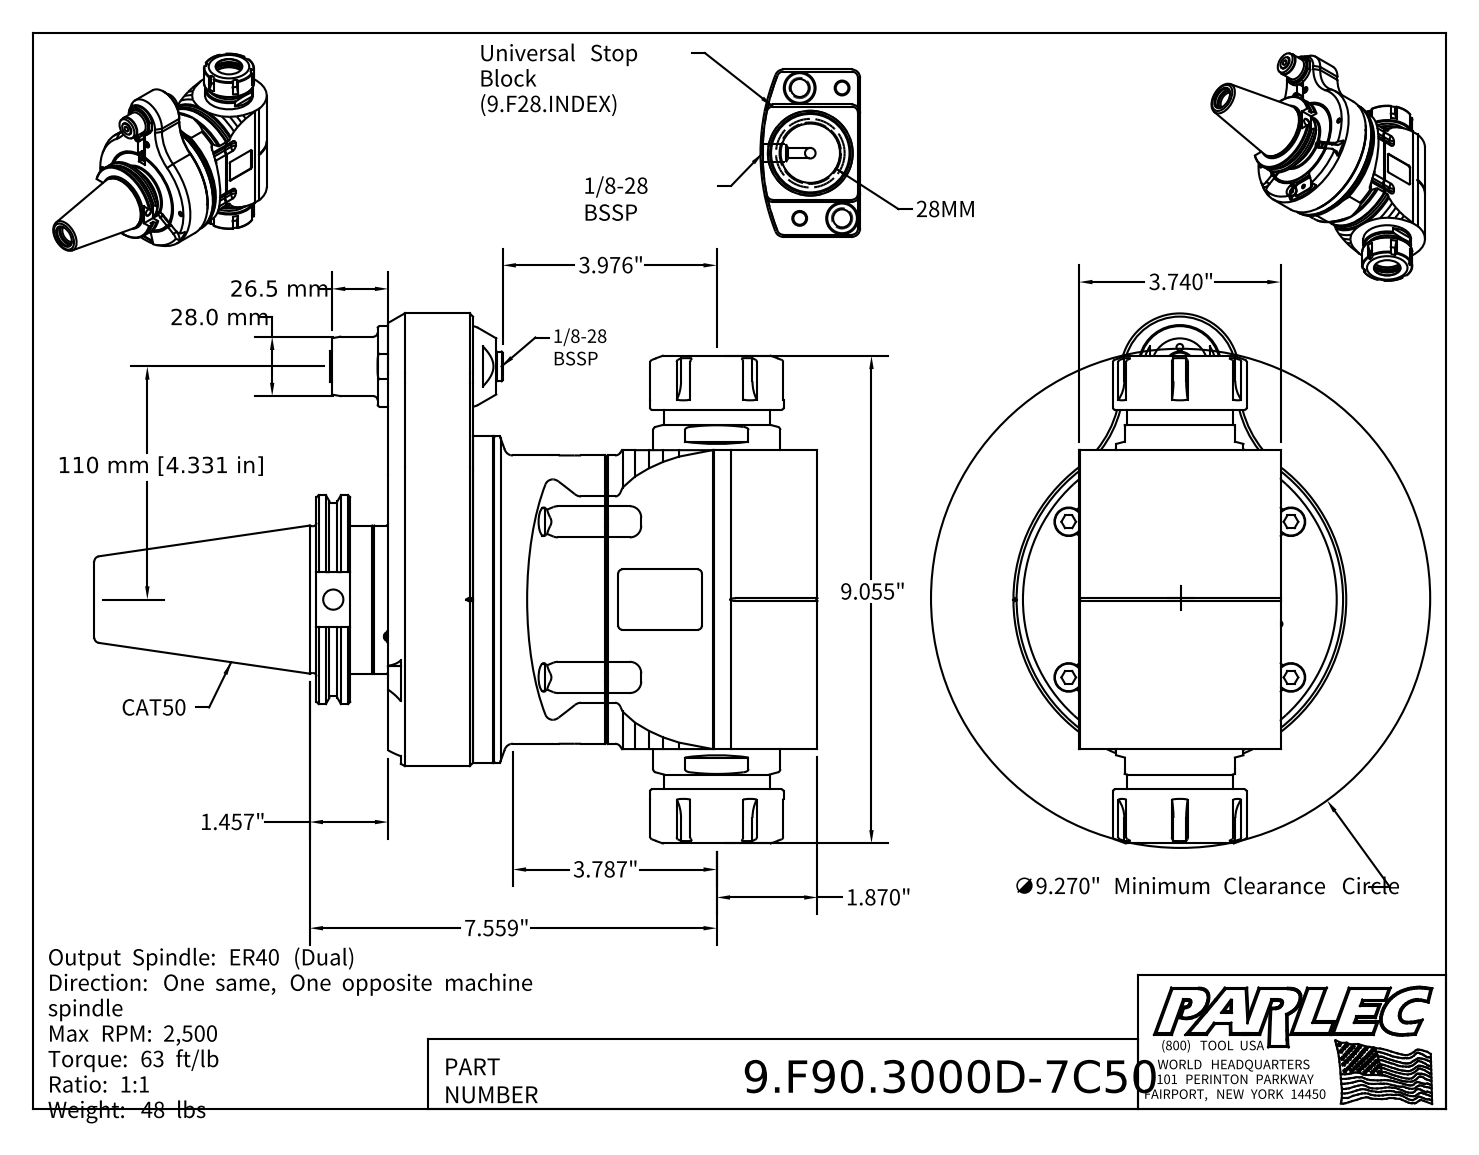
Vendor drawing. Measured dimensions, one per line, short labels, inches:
name: 9.F90.3000D-7C50; F90-30D; 9GA32C_451 (Type 3, Cat50, 110mm, 28x26.5P)
written by: Autodesk Inventor 2022 (AUTOMOTIVE_DESIGN)
unit: in
bodies: 4 solids, 881 faces (378 planar, 241 cylindrical, 262 other)
size: 13.429 × 9.843 × 6.181
volume: 210.6 in³; area: 514.6 in²
holes: 4× ⌀0.197, 4× ⌀0.266, 4× ⌀0.335, 4× ⌀0.531, 3× ⌀0.165, 2× ⌀0.126, 2× ⌀0.13, 2× ⌀0.315, 1× ⌀0.098, 1× ⌀0.236, 1× ⌀0.256, 1× ⌀0.347
bosses: 4× ⌀0.512, 2× ⌀0.551, 2× ⌀0.394, 2× ⌀0.098, 1× ⌀6.063, 1× ⌀5.669, 1× ⌀4.634, 1× ⌀4.398
rounds: 12× R0.039, 12× R0.079, 12× R0.276, 12× R0.591, 6× R0.118, 4× R0.157, 4× R0.197, 4× R0.394
face distances: 1.378, 0.197, 1.181, 0.315, 0.236, 0.571, 0.61, 0.768, 3.74, 0.039
hole spacings: 2.52, 3.563, 3.705, 4.994, 0.197, 0.354, 0.622, 0.709
